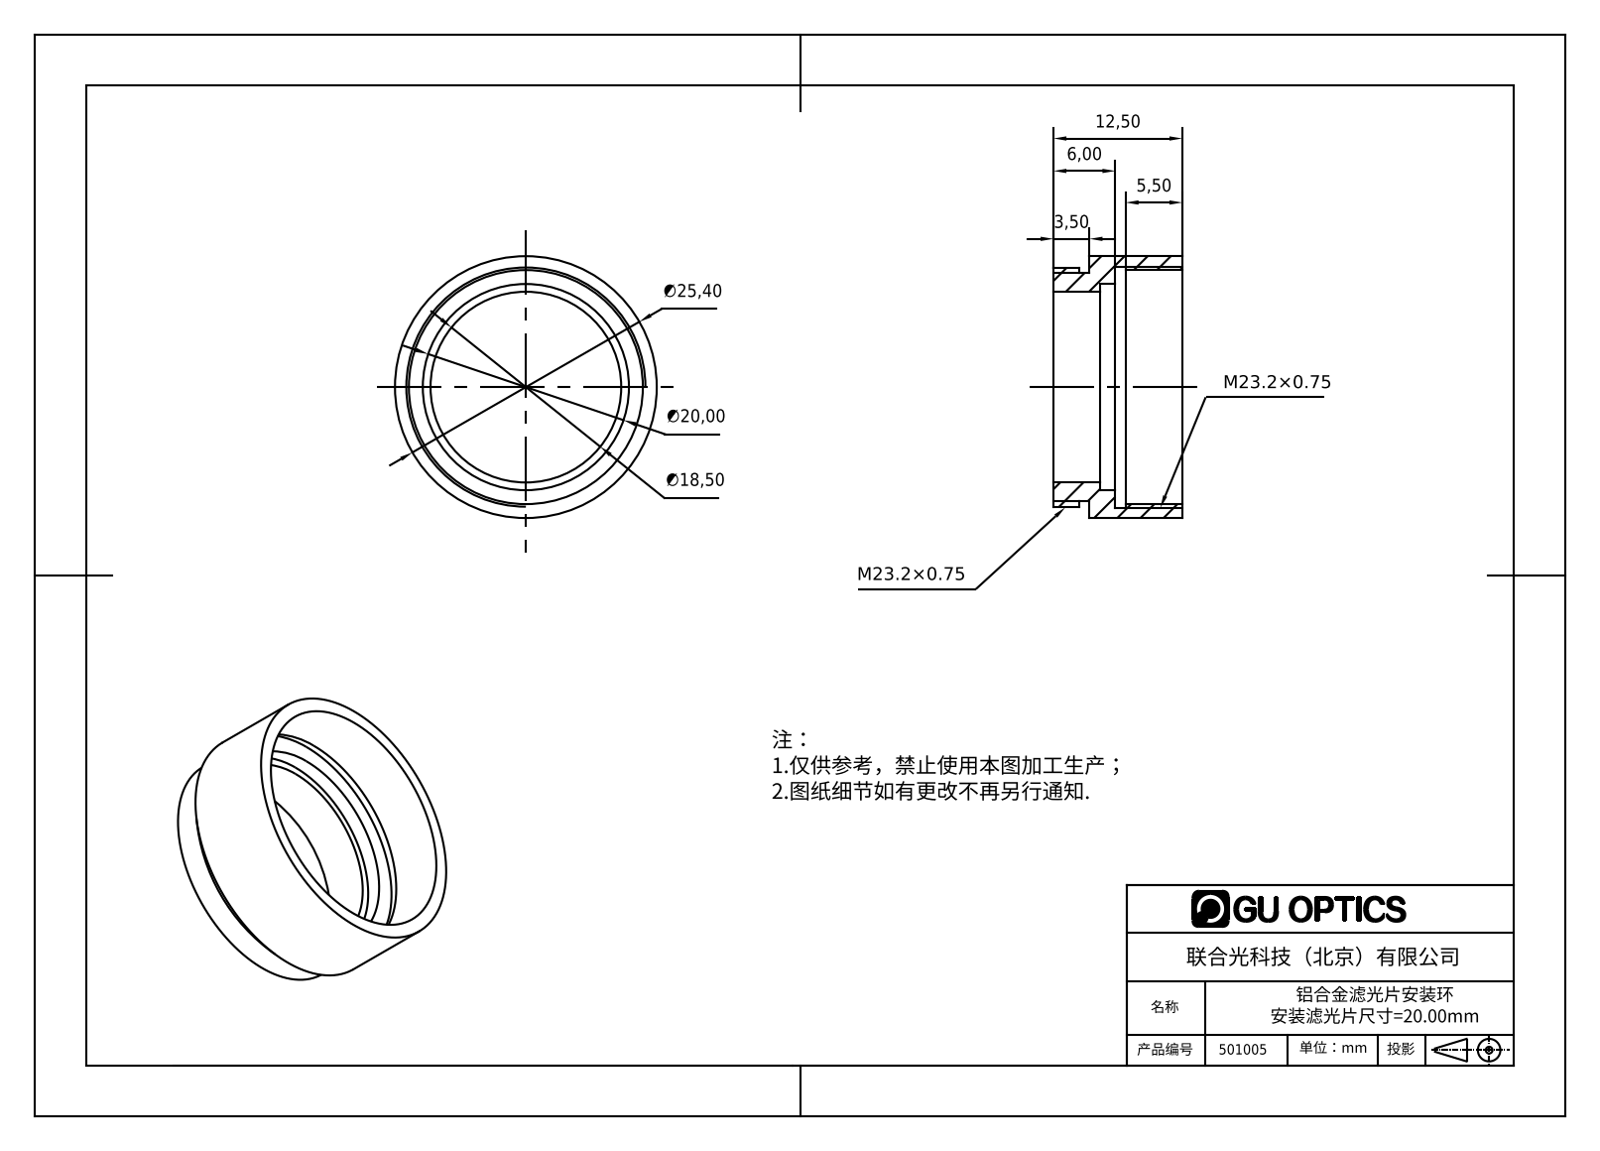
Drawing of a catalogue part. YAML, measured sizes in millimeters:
part_name: "501005"
step_written_by: "SolidWorks 2016 (CONFIG_CONTROL_DESIGN)"
units: millimeters
bodies: {solids: 1, faces: 21, planar: 7, cylindrical: 14, other: 0}
overall_size: [25.4, 25.4, 12.5]
volume: 1667
surface_area: 2389
round_holes:
  - {diameter: 18.5, count: 1}
  - {diameter: 20, count: 1}
  - {diameter: 22.7, count: 1}
  - {diameter: 23.4, count: 1}
round_bosses_or_shafts:
  - {diameter: 25.4, count: 1}
  - {diameter: 23.2, count: 1}
  - {diameter: 22.2, count: 1}
face_to_face_distances: [3.5, 2.5, 6, 1, 12.5, 9, 6.5, 4.5, 1.5, 8]
